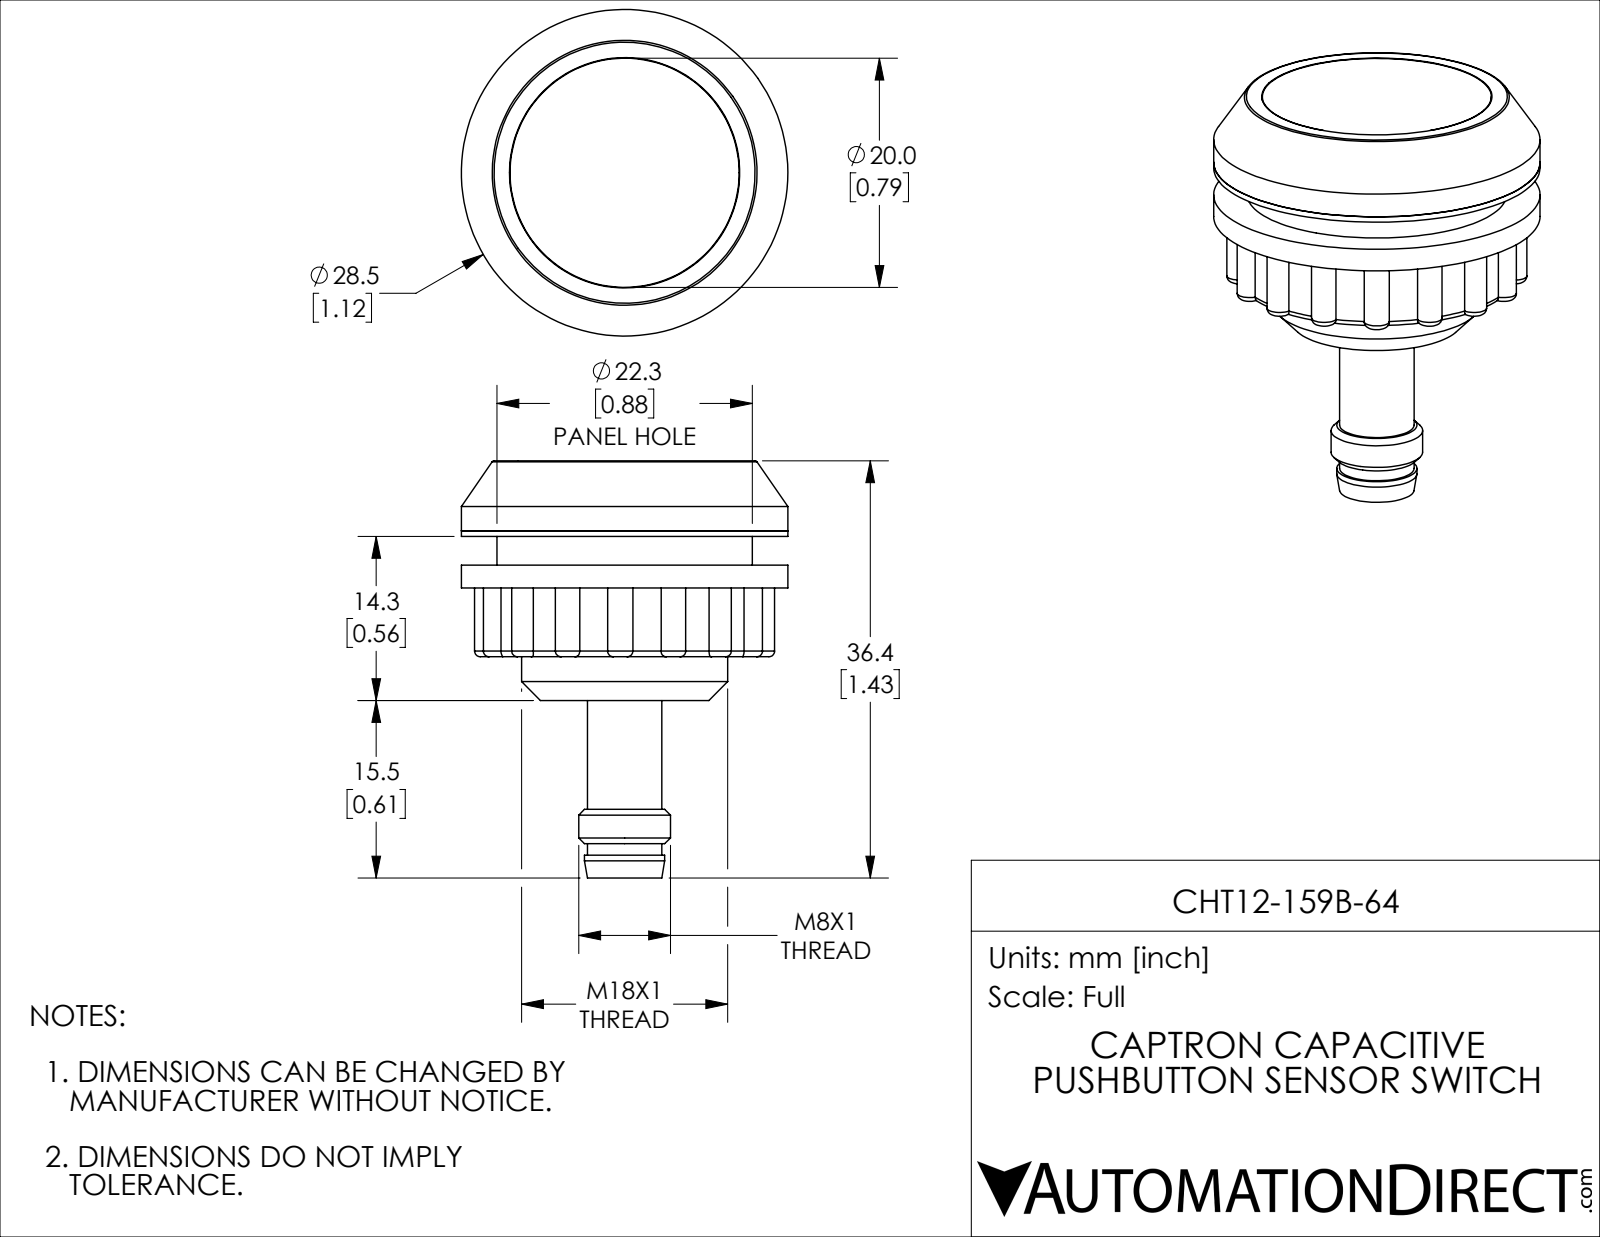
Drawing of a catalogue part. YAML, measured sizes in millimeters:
part_name: "CHT12-159B-64"
step_written_by: "SolidWorks 2019 (CONFIG_CONTROL_DESIGN)"
units: millimeters
bodies: {solids: 10, faces: 192, planar: 25, cylindrical: 91, other: 76}
overall_size: [36.42, 28.5, 28.5]
volume: 10126
surface_area: 7462
round_holes:
  - {diameter: 6, count: 1}
  - {diameter: 14.7, count: 1}
  - {diameter: 17, count: 1}
  - {diameter: 20.1, count: 1}
  - {diameter: 22.3, count: 1}
  - {diameter: 22.6, count: 1}
round_bosses_or_shafts:
  - {diameter: 1, count: 5}
  - {diameter: 28.5, count: 1}
  - {diameter: 18, count: 1}
  - {diameter: 14.4, count: 1}
  - {diameter: 8, count: 1}
  - {diameter: 7, count: 1}
  - {diameter: 6.5, count: 1}
partial_cylinders:
  - {radius: 1.1, count: 16}
  - {radius: 12, count: 1}
face_to_face_distances: [3, 6.08, 6.58, 3.85, 3.08, 0.77, 2.23, 10.5, 2, 4]
